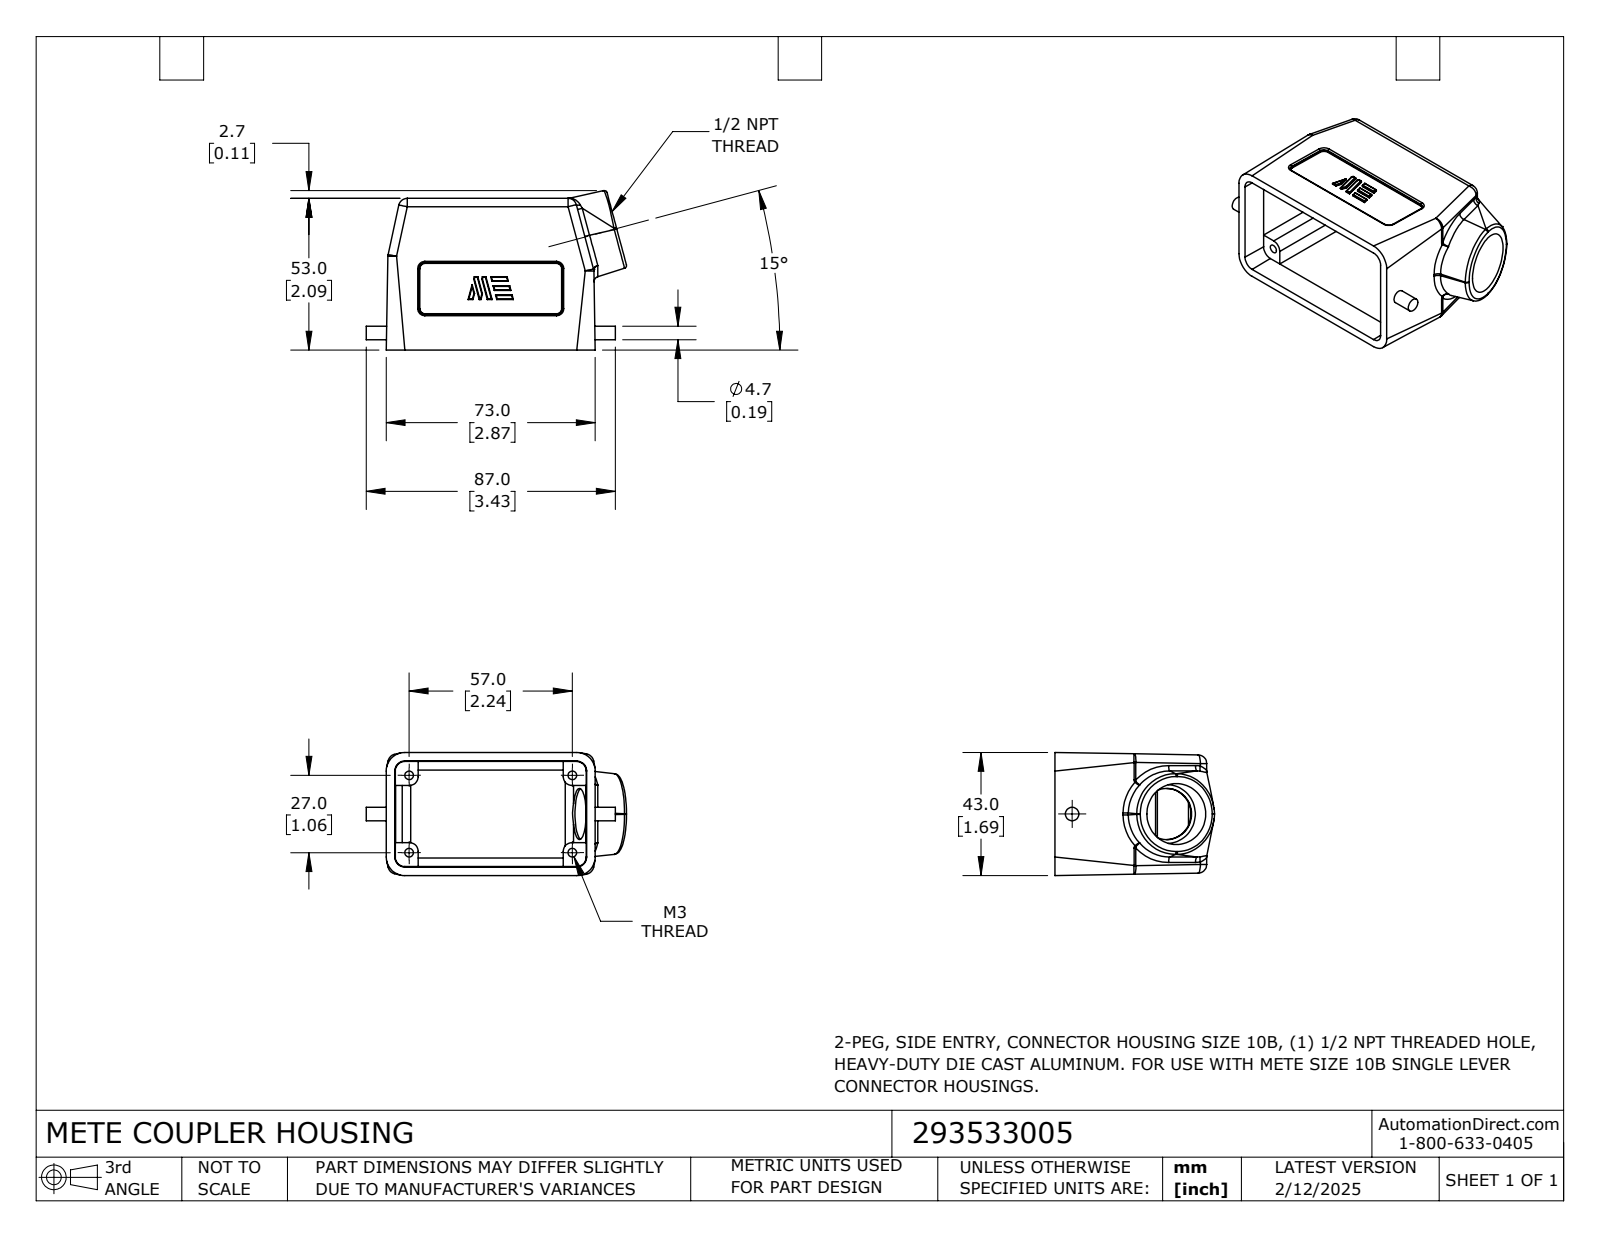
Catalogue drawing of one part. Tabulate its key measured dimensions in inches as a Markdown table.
| quantity | value |
| --- | --- |
| part name | 293533005 |
| STEP written by | SolidWorks 2024 (CONFIG_CONTROL_DESIGN) |
| units | inches |
| bodies | 1 solid, 299 faces (121 planar, 119 cylindrical, 59 other) |
| overall size | 3.579 × 2.194 × 1.693 |
| volume | 2.955 in³ |
| surface area | 44.41 in² |
| round holes (diameter × count) | 0.118 × 4, 0.703 × 1 |
| round bosses / shafts (diameter × count) | 0.185 × 1 |
| partial cylindrical surfaces (radius × count) | 0.008 × 43, 0.118 × 17, 0.02 × 8, 0.079 × 8, 0.075 × 4, 0.039 × 3, 0.098 × 2 |
| main face-to-face distances | 1.444, 0.157, 0.118, 0.04, 0.078, 0.315, 2.31, 0.328, 1.116, 1.929 |
| hole center spacings | 1.063, 2.244, 2.483 |
